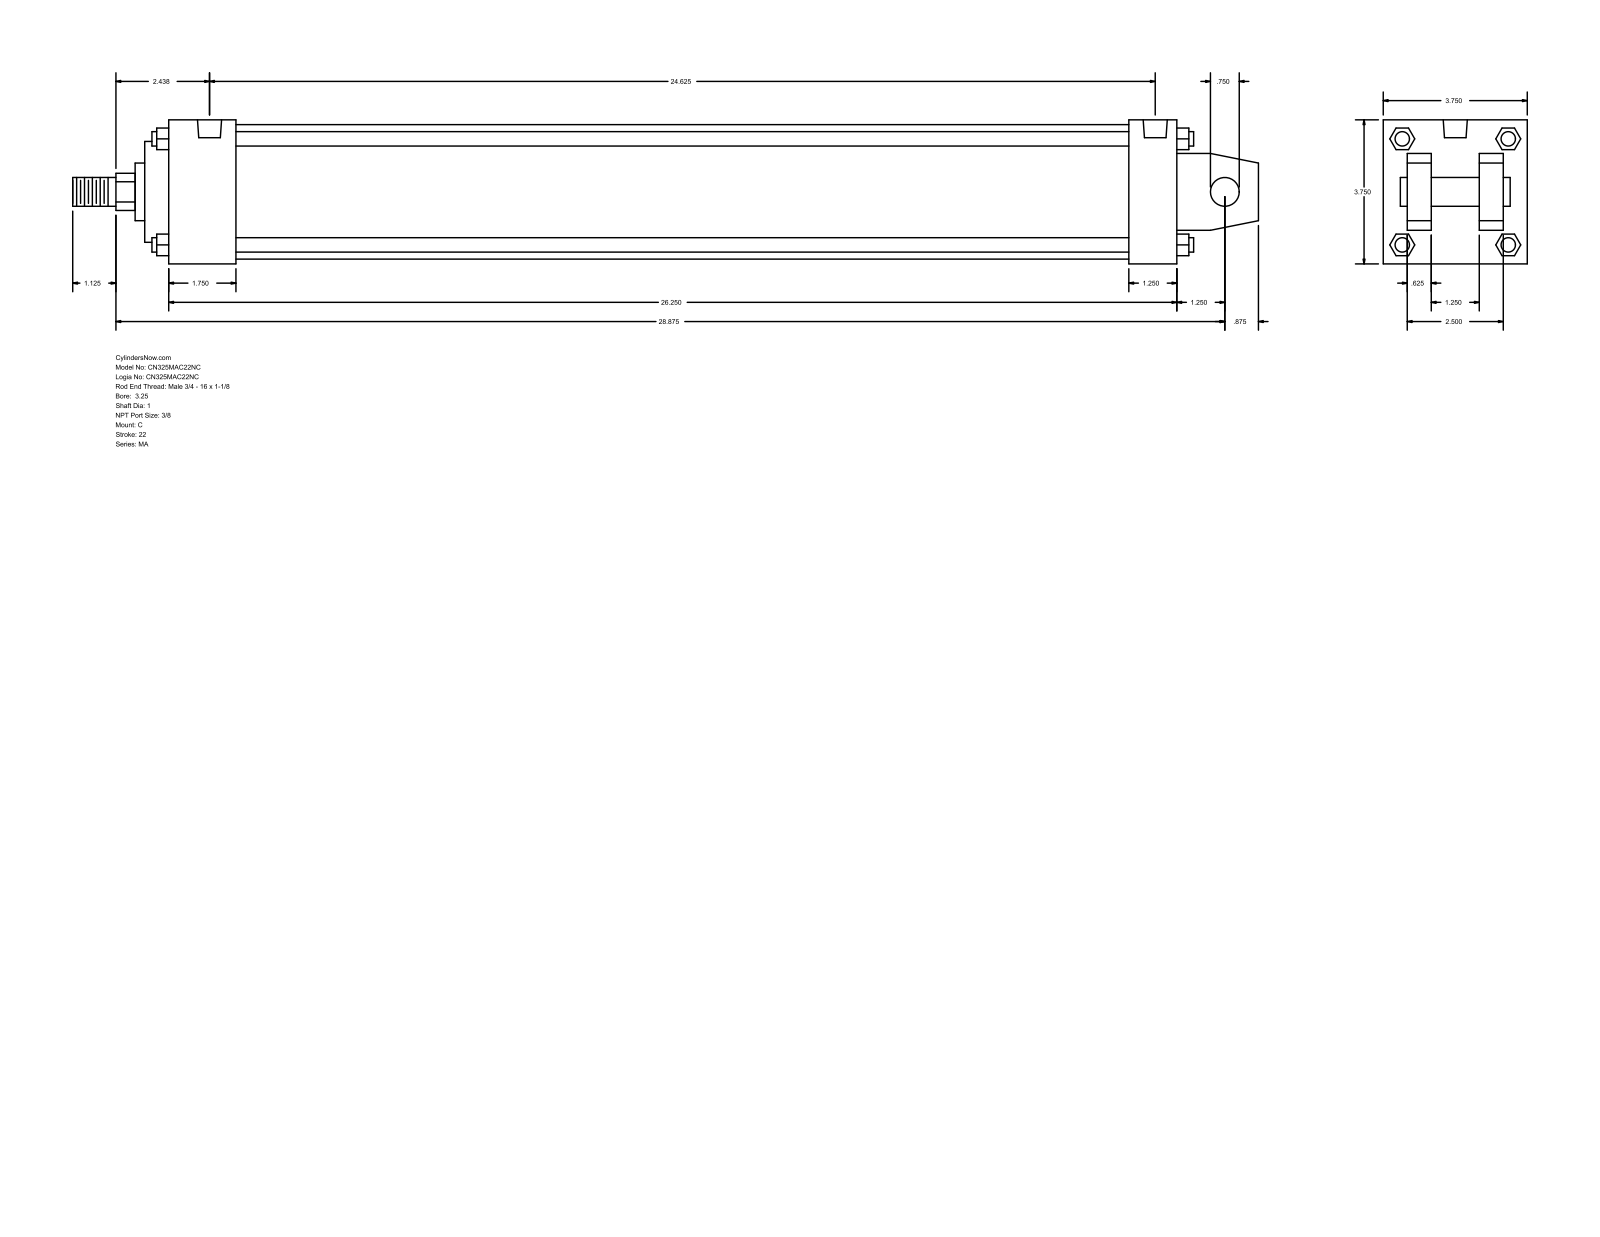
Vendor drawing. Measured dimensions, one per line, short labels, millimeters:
name: MA_C__0325_1
written by: GSSL Pune (CONFIG_CONTROL_DESIGN)
unit: mm
bodies: 0 solids, 141 faces (109 planar, 32 cylindrical, 0 other)
size: 784.23 × 95.25 × 95.25
holes: 4× ⌀11.11, 2× ⌀15.93
bosses: 4× ⌀9.53, 2× ⌀19.05, 1× ⌀88.9, 1× ⌀66.67, 1× ⌀38.1, 1× ⌀25.4
rounds: 1× R12.29
face distances: 95.24, 15.87, 63.5, 666.75, 31.74, 79.37, 47.63, 682.62, 635, 31.75
hole spacings: 615.95, 4.76, 4.77, 620.71, 620.72, 625.48
